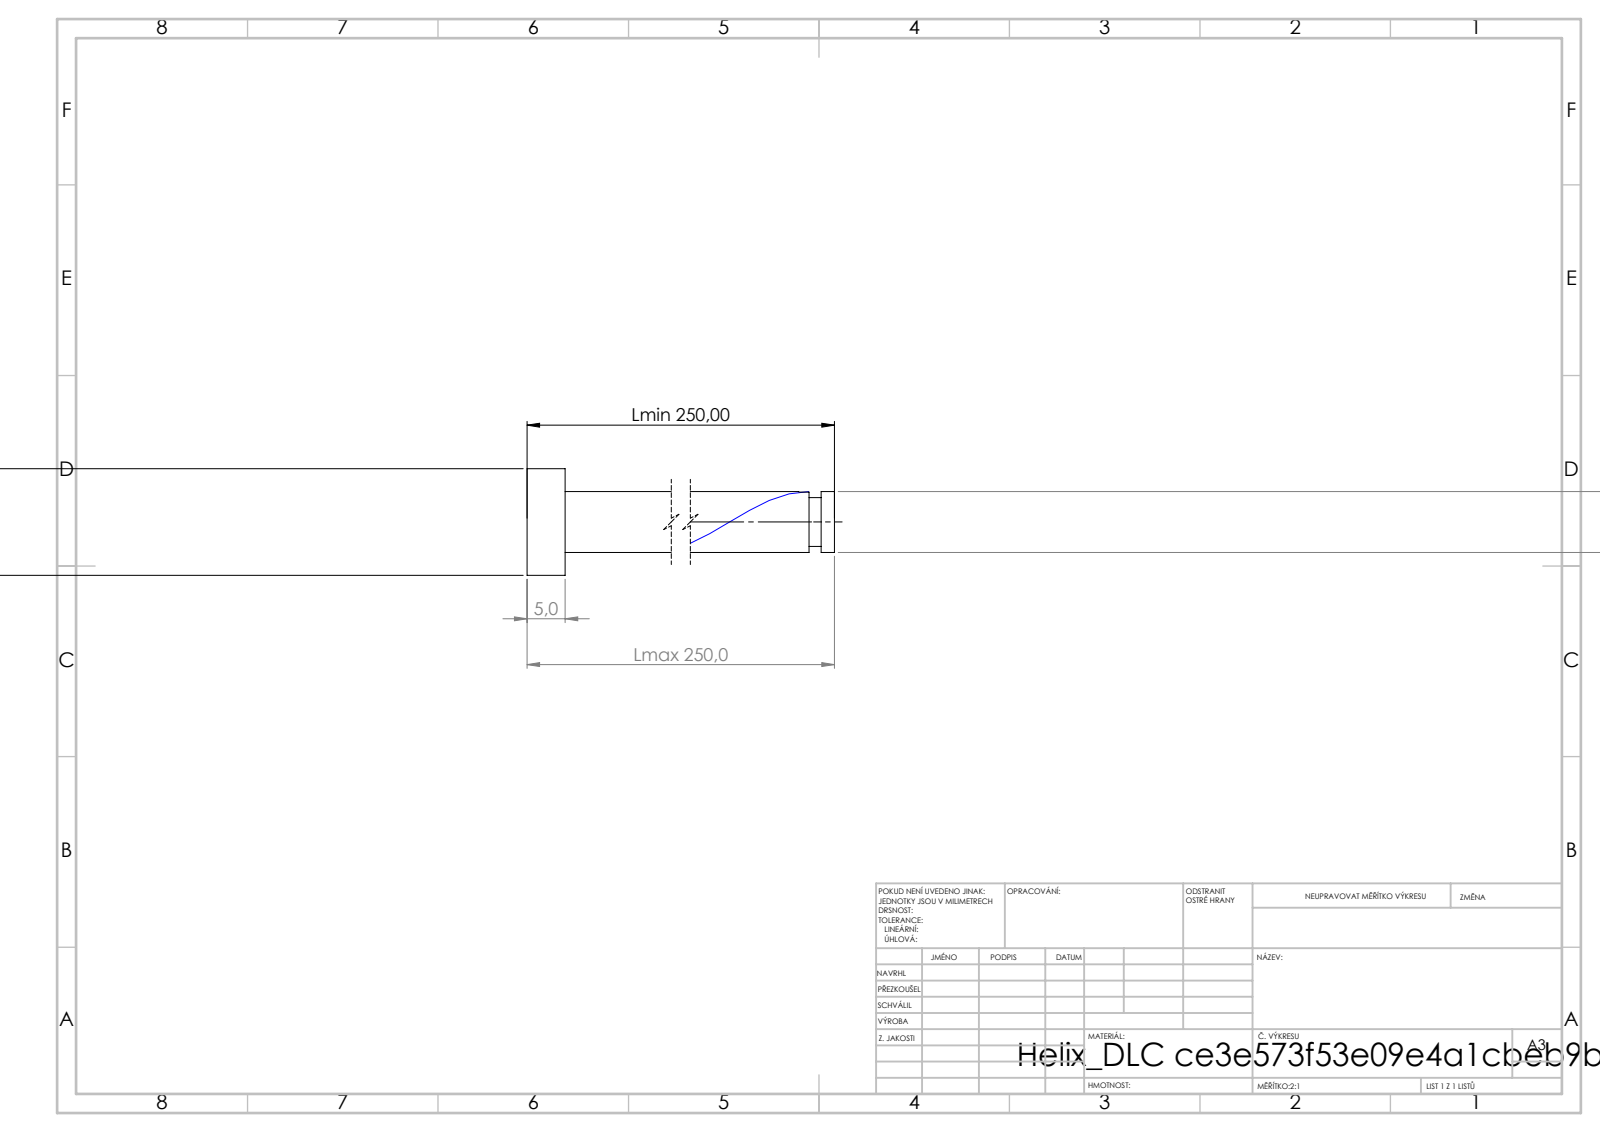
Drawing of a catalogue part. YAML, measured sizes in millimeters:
step_written_by: "SolidWorks 2019 (CONFIG_CONTROL_DESIGN)"
units: millimeters
bodies: {solids: 1, faces: 21, planar: 6, cylindrical: 14, other: 1}
overall_size: [250, 14, 14]
volume: 12935
surface_area: 6831
round_bosses_or_shafts:
  - {diameter: 14, count: 1}
  - {diameter: 8, count: 1}
  - {diameter: 6.4, count: 1}
face_to_face_distances: [5, 250, 245, 248.26, 243.26, 1.74, 246.66, 241.66, 1.6, 3.34]
